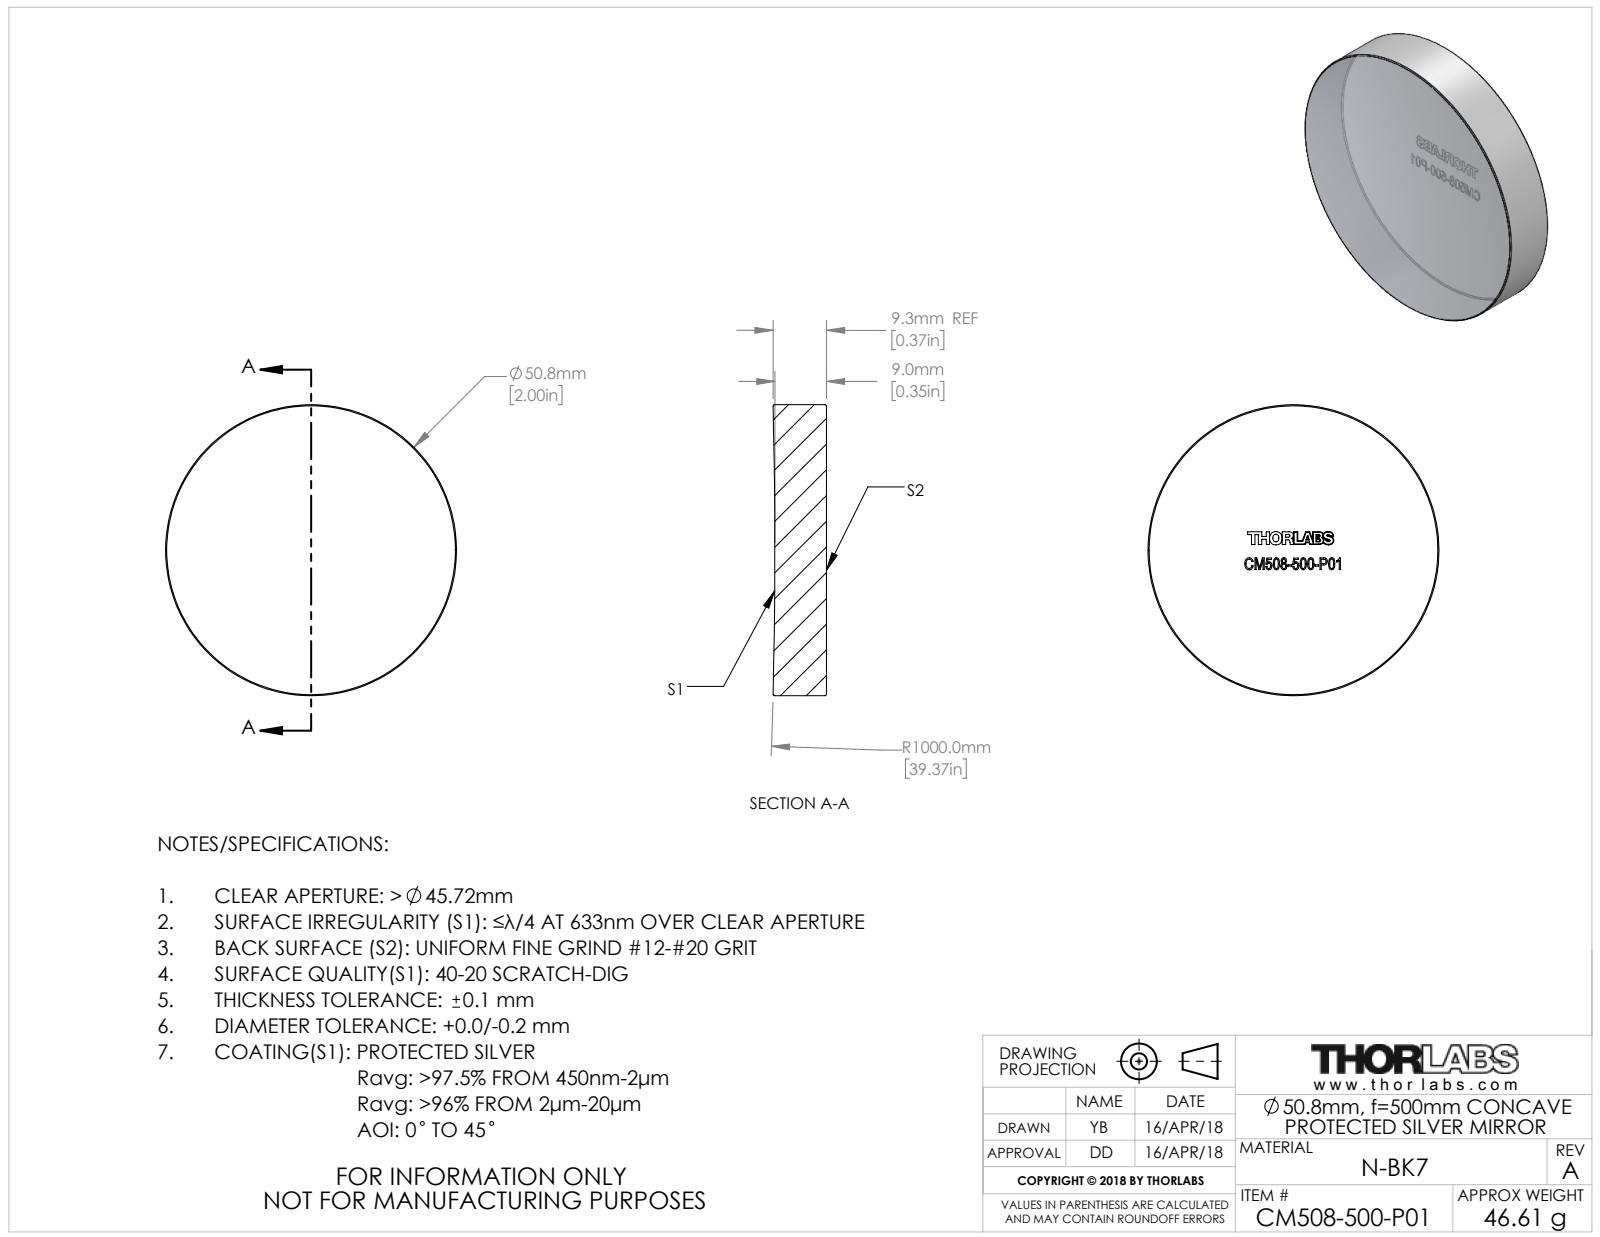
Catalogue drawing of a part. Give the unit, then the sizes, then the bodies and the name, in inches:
Units: inches
Overall size (bounding box): 2 × 2 × 0.367
Round bosses / shafts (diameter × count): ⌀2 ×1
Volume: 1.133 in³ · Surface area: 8.531 in²
Bodies: 1 solid, 44 faces (36 planar, 2 cylindrical, 6 other)
Part name (STEP PRODUCT): TTN153326-E0W
STEP written by: SolidWorks 2018 (CONFIG_CONTROL_DESIGN)
